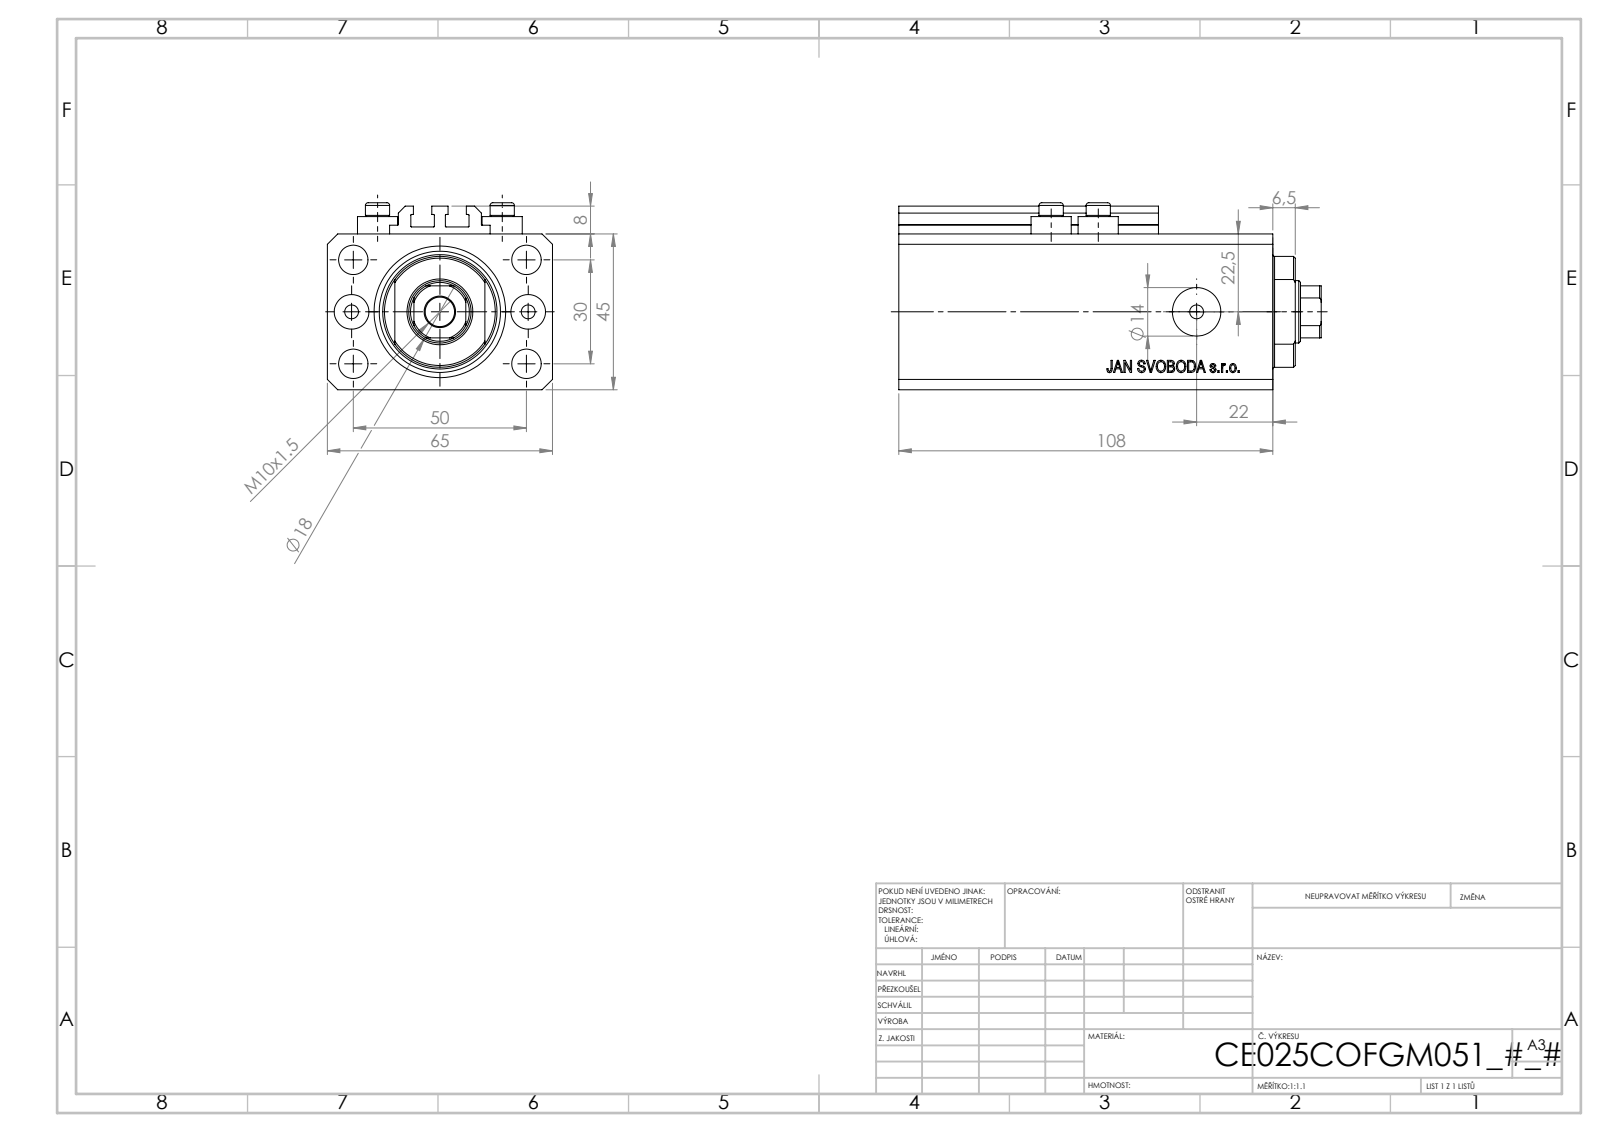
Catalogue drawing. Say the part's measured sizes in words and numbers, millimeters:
The part is named "V250CE_VC_C; ALLEN BOLT V250CE; V250CE_C_VCP; V250CE_C_Body". Its 3-D file was written by "SolidWorks 2019 (CONFIG_CONTROL_DESIGN)". It is 8 solids with 1034 faces: 504 planar, 86 cylindrical and 444 other. Overall it measures 122 by 65 by 54 millimeters. Its volume is 291 603 cubic millimeters and its surface area 74 491 square millimeters. Round holes: 8 of diameter 4, 5 of diameter 8.5, 2 of diameter 10, 2 of diameter 14, 1 of diameter 18, 1 of diameter 25, 1 of diameter 38. Round bosses or shafts: 4 of diameter 11.6, 4 of diameter 7. Partial cylindrical surfaces (rounded edges, fillets, slot ends): 10 of radius 0.2, 1 of radius 8.5, 1 of radius 16. The main face-to-face distances are 45, 65, 14, 94, 108, 47, 2.5, 20.5, 10, 2. The hole center spacings are 15.01, 29.15, 52.68, 13.6, 25.5, 30, 36, 38.48.
